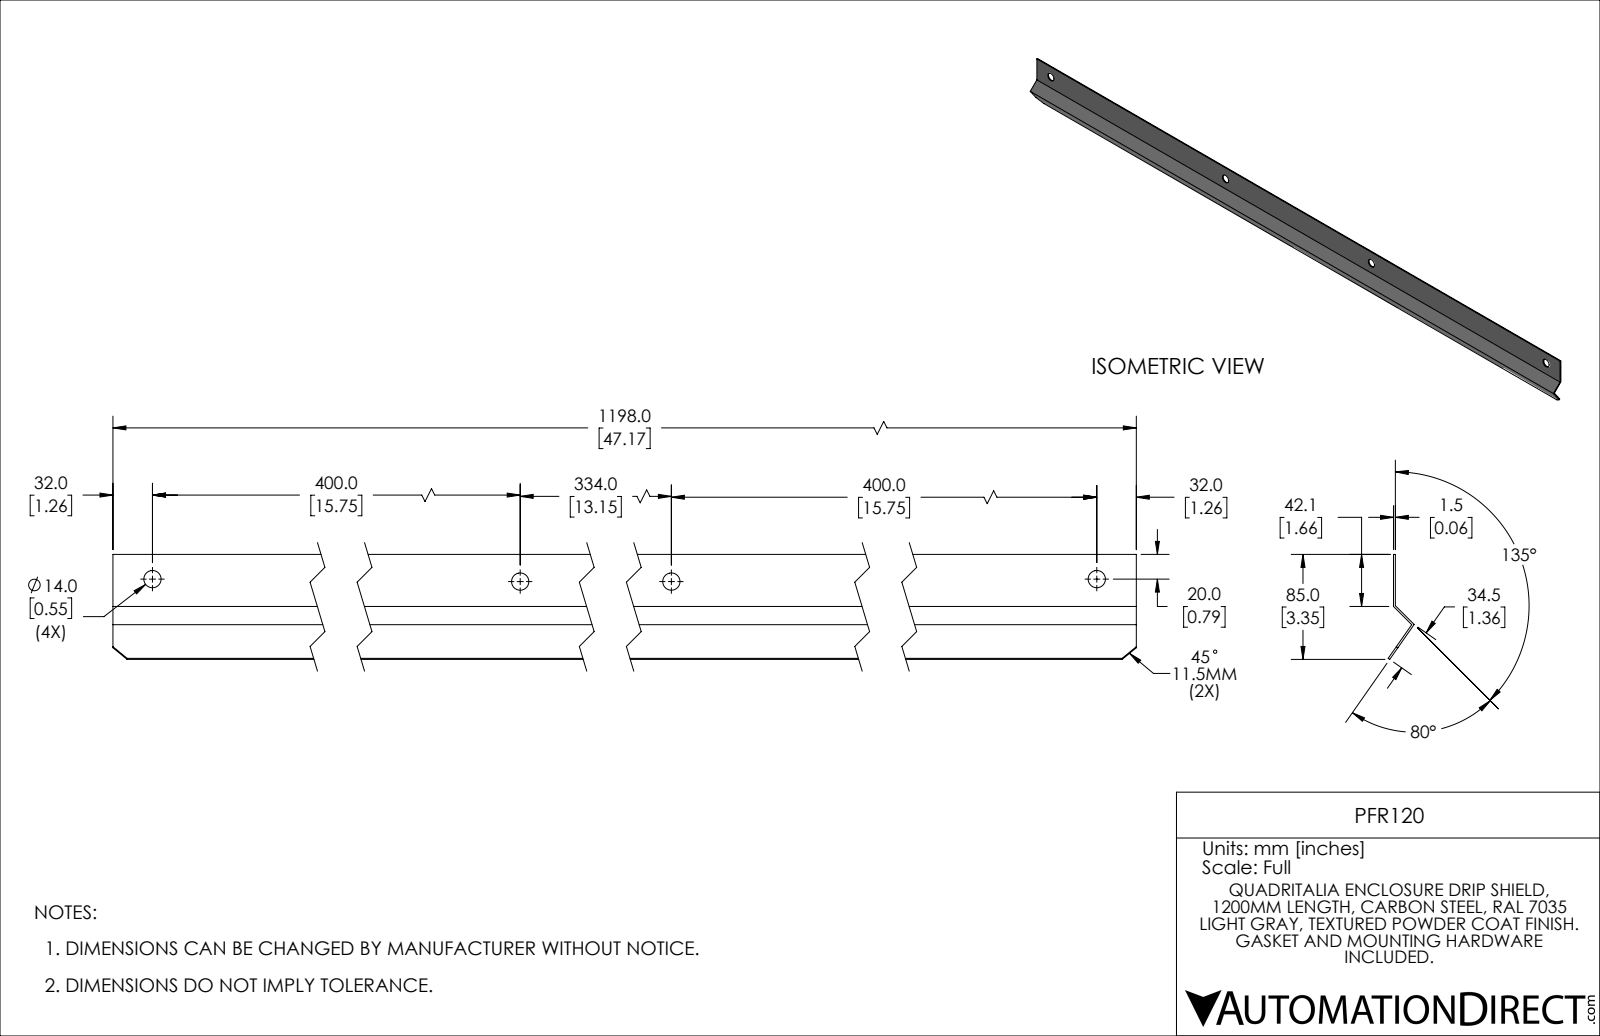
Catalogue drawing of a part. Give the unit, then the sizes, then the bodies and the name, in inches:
Units: inches
Overall size (bounding box): 47.165 × 3.345 × 0.827
Round holes (diameter × count): ⌀0.551 ×4
Main face-to-face distances: 0.059, 47.165
Hole centre spacings: 15.748, 28.898, 13.15, 44.646
Volume: 10.55 in³ · Surface area: 363.8 in²
Bodies: 1 solid, 16 faces (12 planar, 4 cylindrical, 0 other)
Part name (STEP PRODUCT): PFR120
STEP written by: SolidWorks 2021 (CONFIG_CONTROL_DESIGN)
